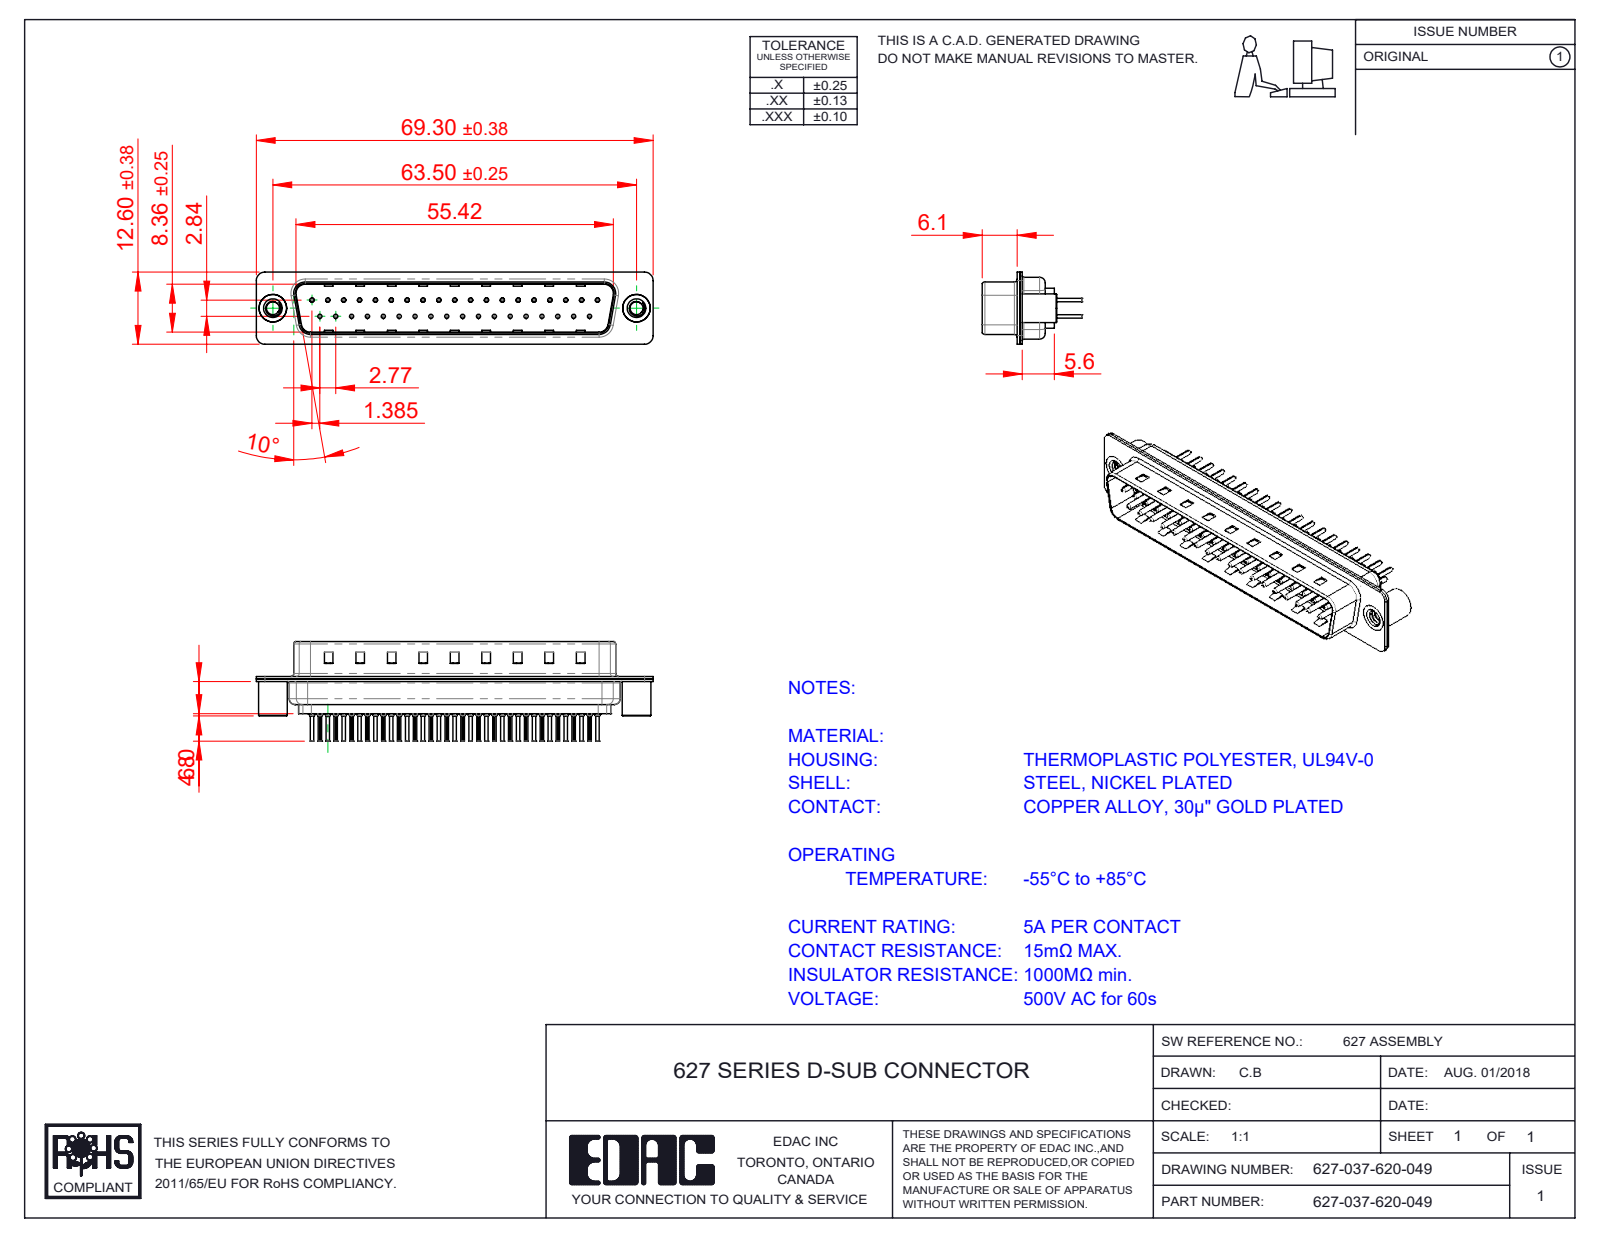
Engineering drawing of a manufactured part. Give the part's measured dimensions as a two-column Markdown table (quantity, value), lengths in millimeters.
| quantity | value |
| --- | --- |
| part name | 627-037-620-049; 627 Shell Rear_37 Contacts; 627 Shell Front_37 Contacts; 627 Contact Row 1_20L (+3 more) |
| STEP written by | SolidWorks 2020 (CONFIG_CONTROL_DESIGN) |
| units | millimeters |
| bodies | 42 solids, 4060 faces (1091 planar, 1530 cylindrical, 1439 other) |
| overall size | 69.3 × 17.3 × 12.6 |
| volume | 3 798 mm³ |
| surface area | 10 871 mm² |
| round holes (diameter × count) | 0.2 × 37, 0.35 × 37, 1.1 × 37, 1.6 × 37, 2.26 × 2, 4 × 2, 4.8 × 2 |
| round bosses / shafts (diameter × count) | 2 × 37, 1.5 × 37, 0.75 × 37, 0.6 × 37, 5 × 2, 4.9 × 2 |
| partial cylindrical surfaces (radius × count) | 0.1 × 74, 1.5 × 16, 2 × 12, 0.5 × 8, 1.6 × 8, 0.25 × 4, 0.6 × 4, 0.65 × 4 |
| main face-to-face distances | 0.4, 0.82, 9.58, 0.45, 8.76, 1.5, 0.9, 1.4, 6.5, 6.05 |
| hole center spacings | 3.16, 2.77, 5.54, 8.31, 5.04, 10.1, 11.08, 12.78 |
